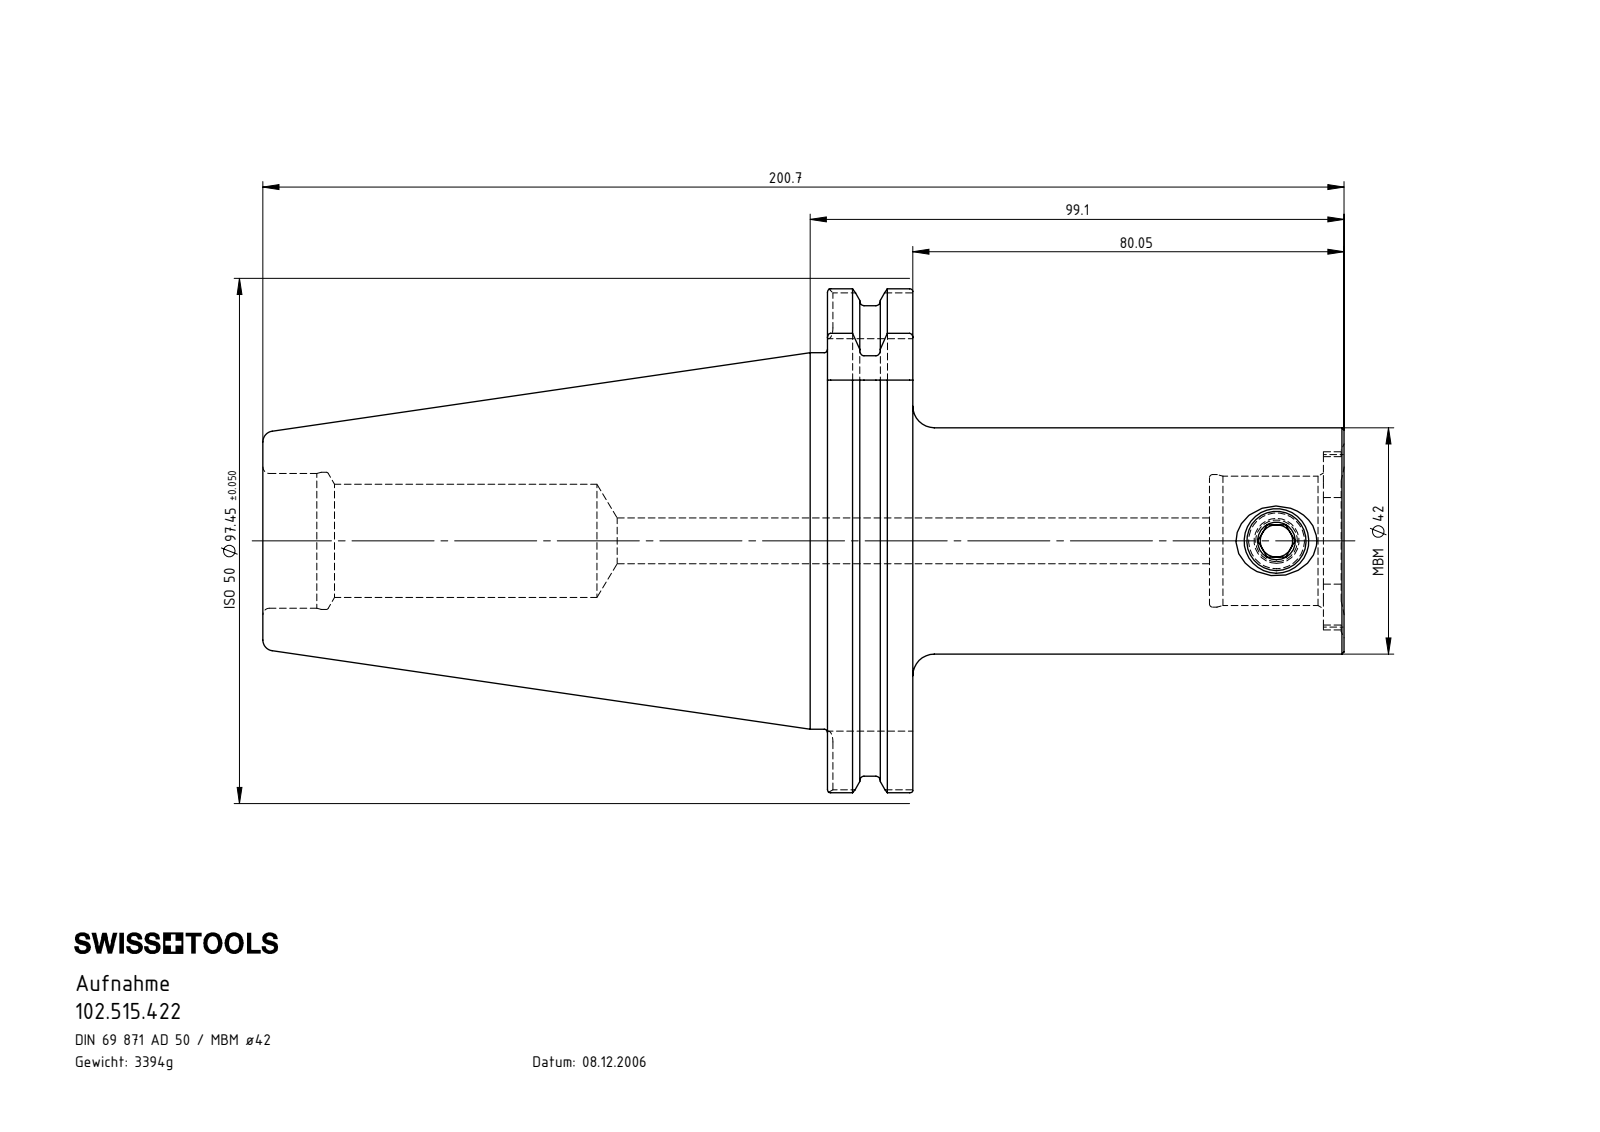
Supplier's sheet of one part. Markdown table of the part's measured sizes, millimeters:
| quantity | value |
| --- | --- |
| part name | MB4-ER1.001.013_A; 102.515.422; SK5-MB4.K01.099_C |
| STEP written by | SolidWorks 2017 (CONFIG_CONTROL_DESIGN) |
| units | millimeters |
| bodies | 2 solids, 172 faces (55 planar, 50 cylindrical, 67 other) |
| overall size | 200.7 × 97.45 × 93.51 |
| volume | 432 375 mm³ |
| surface area | 55 619 mm² |
| round holes (diameter × count) | 6 × 1, 8.5 × 1, 11 × 1, 21 × 1, 24 × 1, 24.6 × 1, 25 × 1, 25.45 × 1 |
| round bosses / shafts (diameter × count) | 91 × 1, 69.85 × 1, 42 × 1, 12 × 1 |
| partial cylindrical surfaces (radius × count) | 2 × 8, 5.2 × 4, 14.9 × 1, 16.52 × 1, 48.73 × 1 |
| main face-to-face distances | 15.85, 104.8, 120.65, 21.15, 175.7, 70.9, 55.05, 72.8, 196.85, 92.05 |
